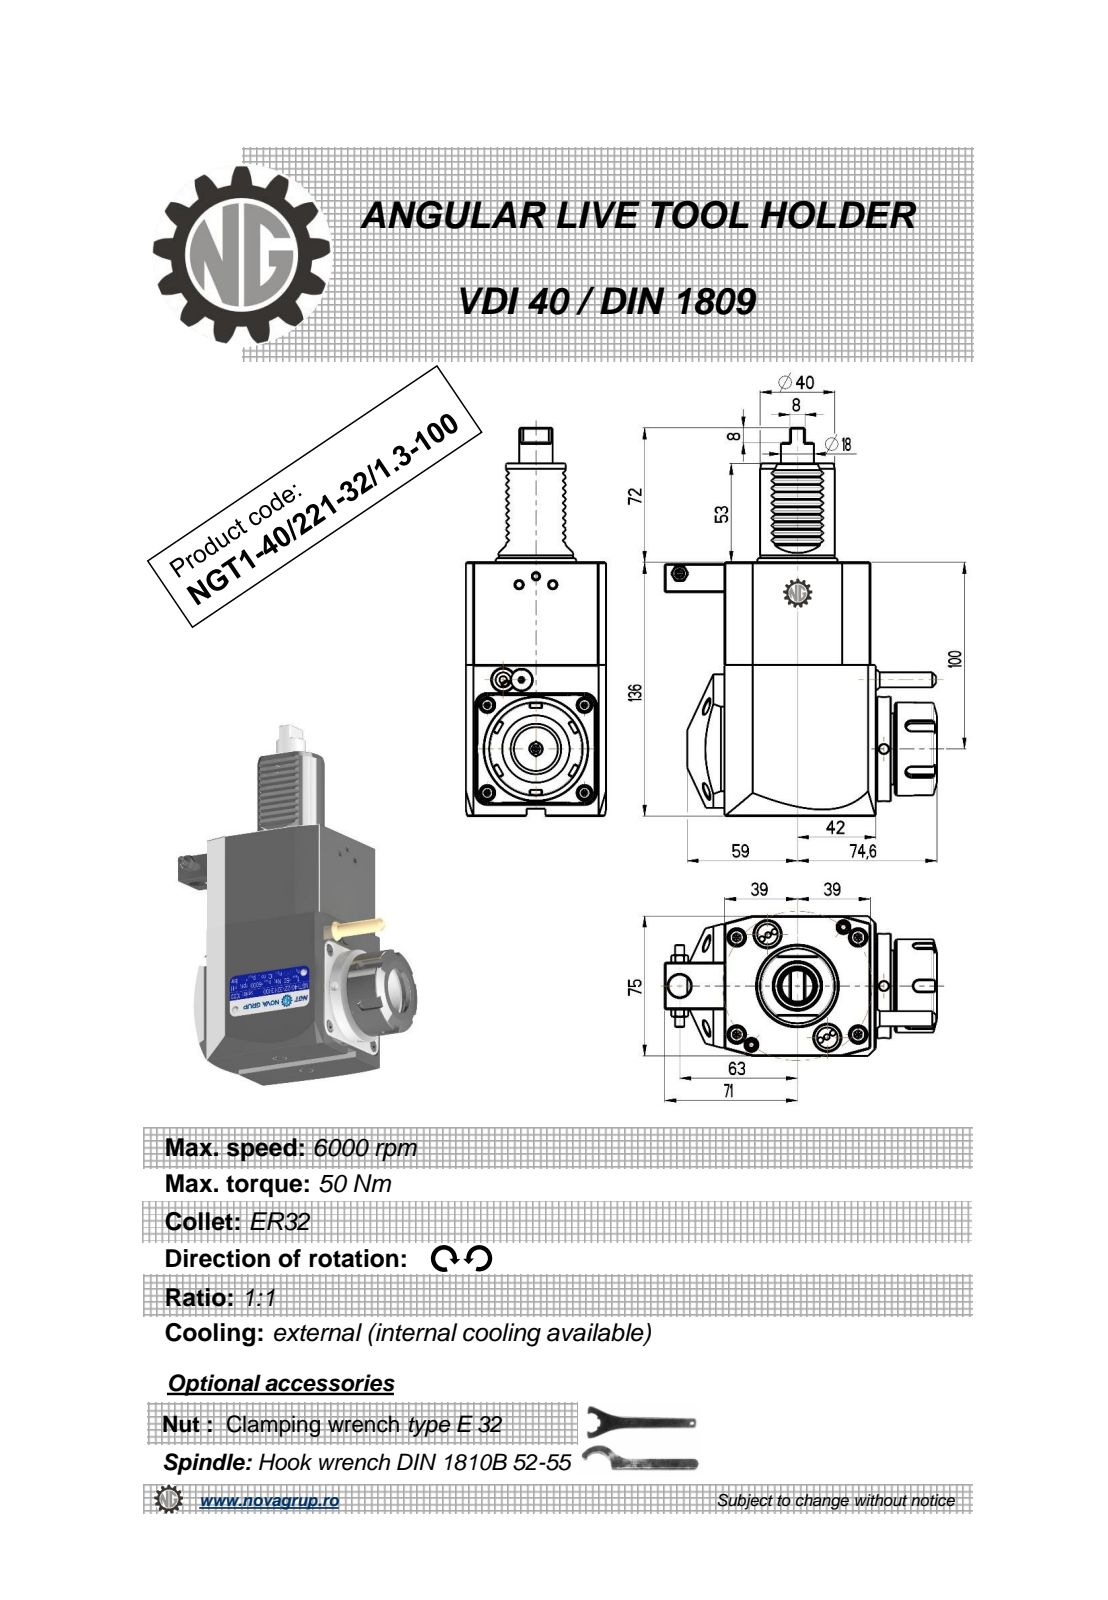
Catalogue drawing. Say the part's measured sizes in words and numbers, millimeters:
The part is named "NGT1_40_221_32_1_3_100". Its 3-D file was written by "PRO/ENGINEER BY PARAMETRIC TECHNOLOGY CORPORATION, 2010280 (CONFIG_CONTROL_DESIGN)". It is 1 solid with 455 faces: 224 planar, 94 cylindrical and 137 other. Overall it measures 208 by 145.6 by 75 millimeters. Its volume is 985 851 cubic millimeters and its surface area 76 879 square millimeters. Round holes: 3 of diameter 5, 1 of diameter 3, 1 of diameter 4.2, 1 of diameter 9.5, 1 of diameter 12, 1 of diameter 27. Round bosses or shafts: 1 of diameter 56, 1 of diameter 50, 1 of diameter 43, 1 of diameter 40, 1 of diameter 17.8, 1 of diameter 11.2, 1 of diameter 8.96, 1 of diameter 8. Partial cylindrical surfaces (rounded edges, fillets, slot ends): 20 of radius 0.3, 12 of radius 0.26, 6 of radius 0.22, 5 of radius 3, 2 of radius 0.8, 1 of radius 40. The main face-to-face distances are 75, 136, 78, 81, 3, 84.88, 80.8, 2.8, 7.5, 11. The hole center spacings are 40.93, 58.19, 92.5, 109.25, 144.12.
